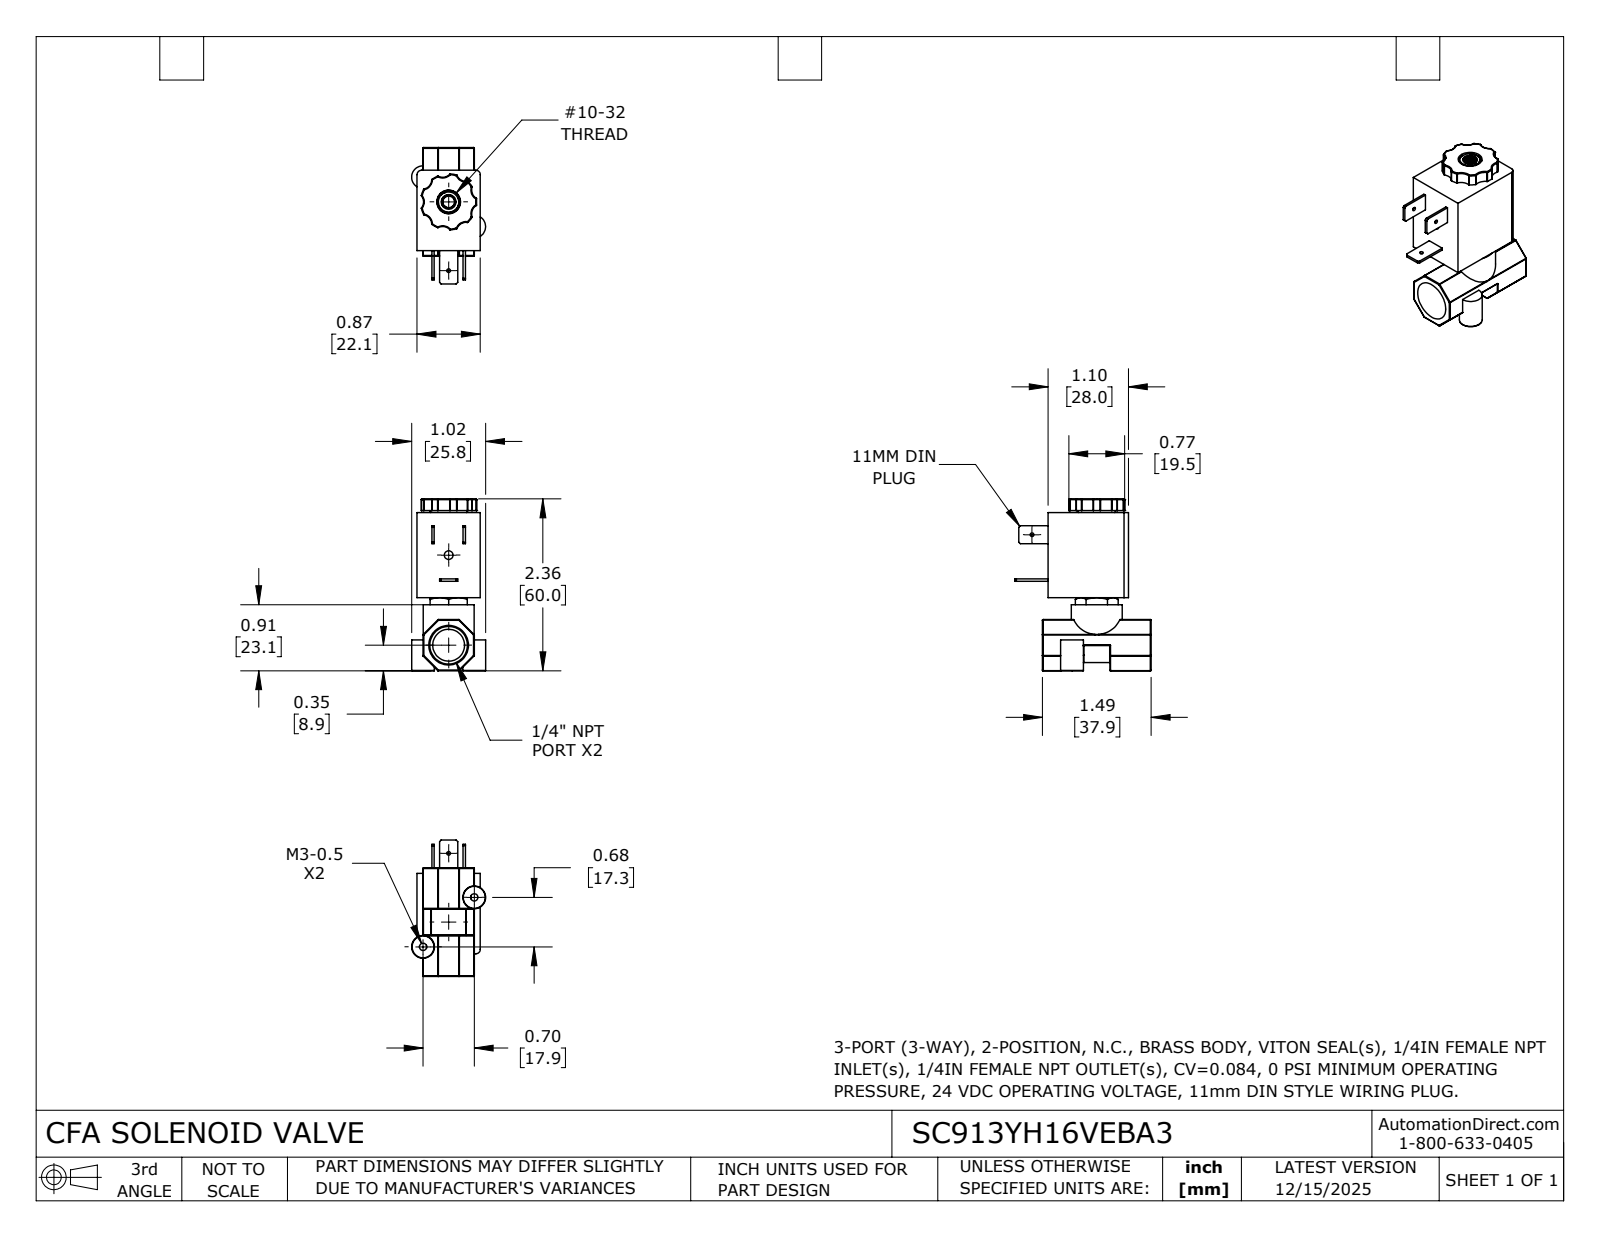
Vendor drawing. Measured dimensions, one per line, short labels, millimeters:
name: SC913YH16VEBA3
written by: SolidWorks 2024 (CONFIG_CONTROL_DESIGN)
unit: mm
bodies: 1 solid, 308 faces (68 planar, 139 cylindrical, 101 other)
size: 60 × 47.6 × 25.8
volume: 27 280 mm³; area: 10 390 mm²
holes: 2× ⌀1.3, 2× ⌀2.5, 1× ⌀3, 1× ⌀4.1, 1× ⌀8.3, 1× ⌀11.1
bosses: 2× ⌀8, 1× ⌀17.8, 1× ⌀8
rounds: 42× R0.3, 14× R0.1, 7× R3.4, 2× R1.5, 2× R3.4, 1× R6, 1× R7.8, 1× R9.8
face distances: 22.1, 17.9, 28, 29.6, 2.1, 20, 25.6, 55.2, 60, 34.5
hole spacings: 12.4, 17.8, 24, 24.9, 31.4, 33.9
